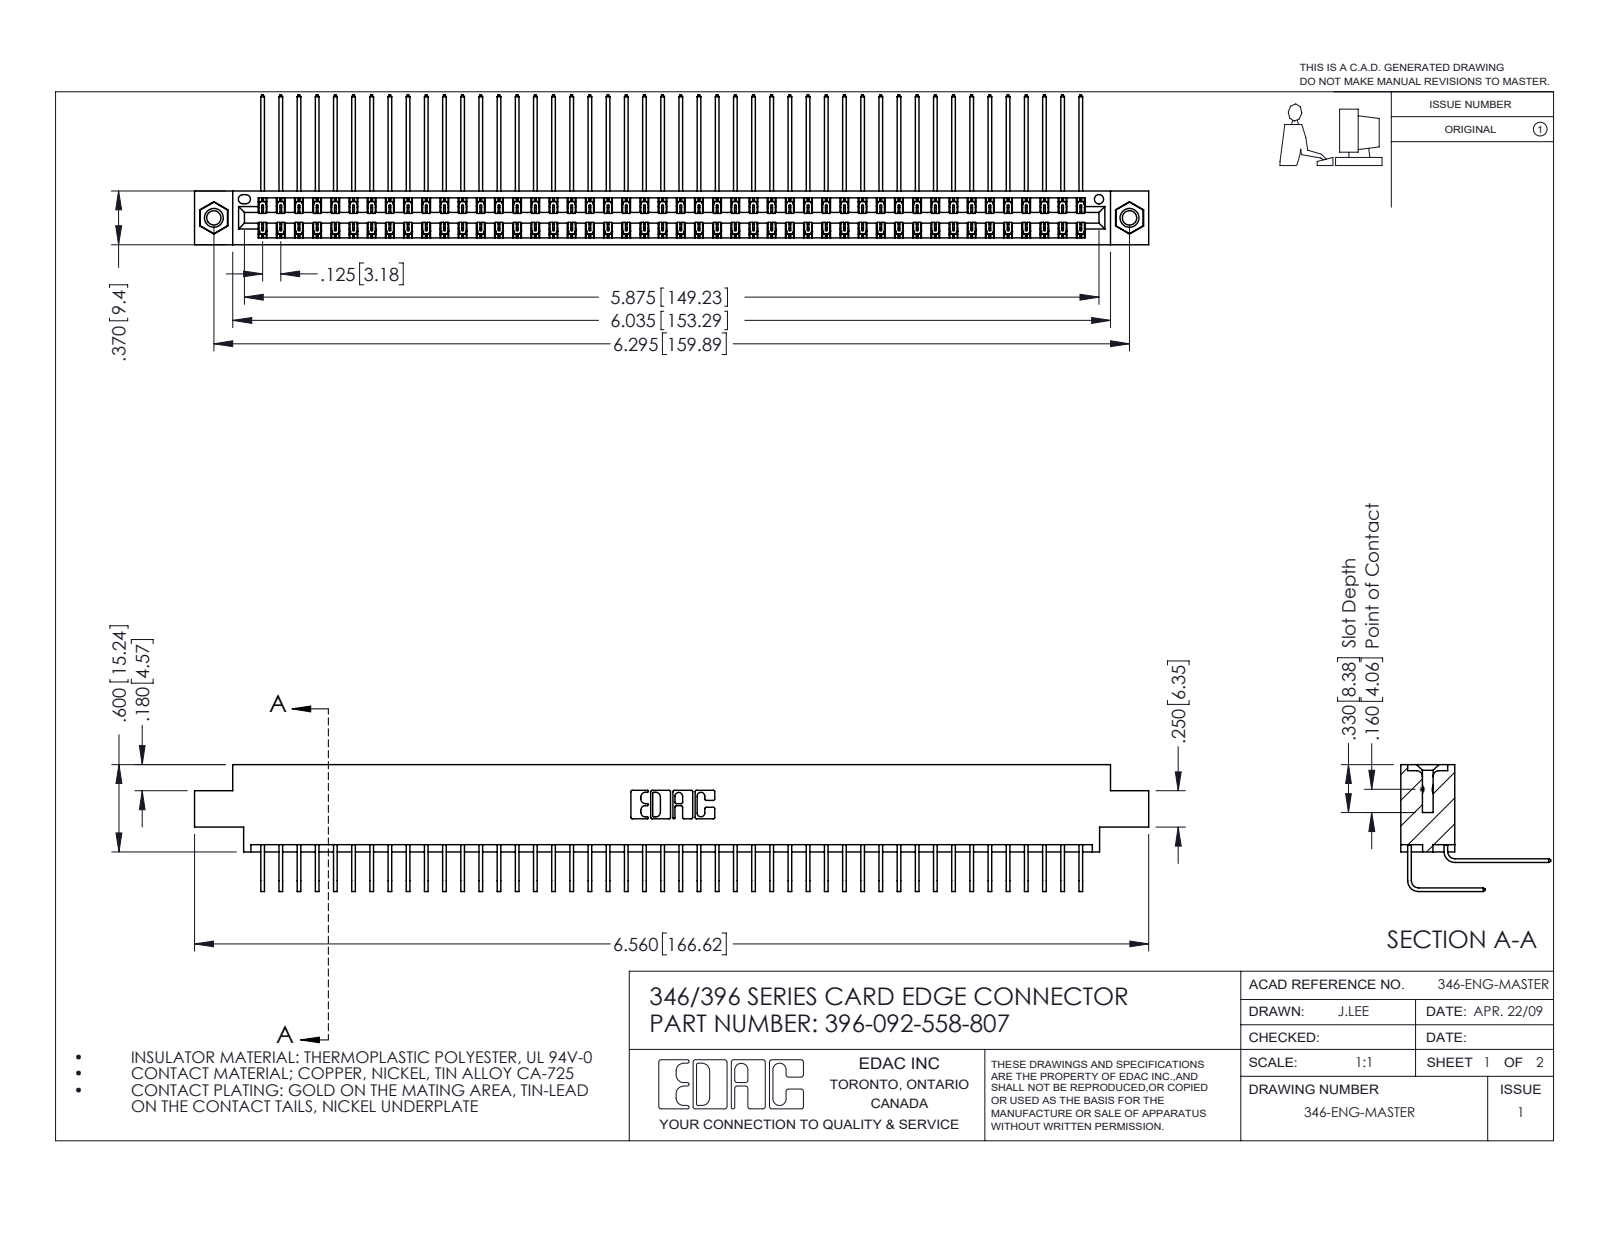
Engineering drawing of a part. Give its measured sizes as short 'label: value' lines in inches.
name: 396-092-558-807; 345-292-001_558 559 Tail - 1; 345-250-001_345-250-005-103; 345-292-001_558 Tail - 2 (+1 more)
written by: SolidWorks 2016 (CONFIG_CONTROL_DESIGN)
unit: in
bodies: 95 solids, 5154 faces (3516 planar, 1622 cylindrical, 16 other)
size: 6.56 × 1.03 × 0.873
volume: 1.016 in³; area: 39.83 in²
holes: 2× ⌀0.098, 2× ⌀0.125, 2× ⌀0.156, 1× ⌀0.064
bosses: 2× ⌀0.155
rounds: 138× R0.006, 22× R0.01, 6× R0.007, 6× R0.031, 3× R0.026, 2× R0.014, 2× R0.022, 2× R0.024
face distances: 0.322, 0.048, 0.025, 0.37, 0.25, 0.298, 0.072, 0.275, 0.222, 0.148
hole spacings: 0.246, 6.086, 6.295
